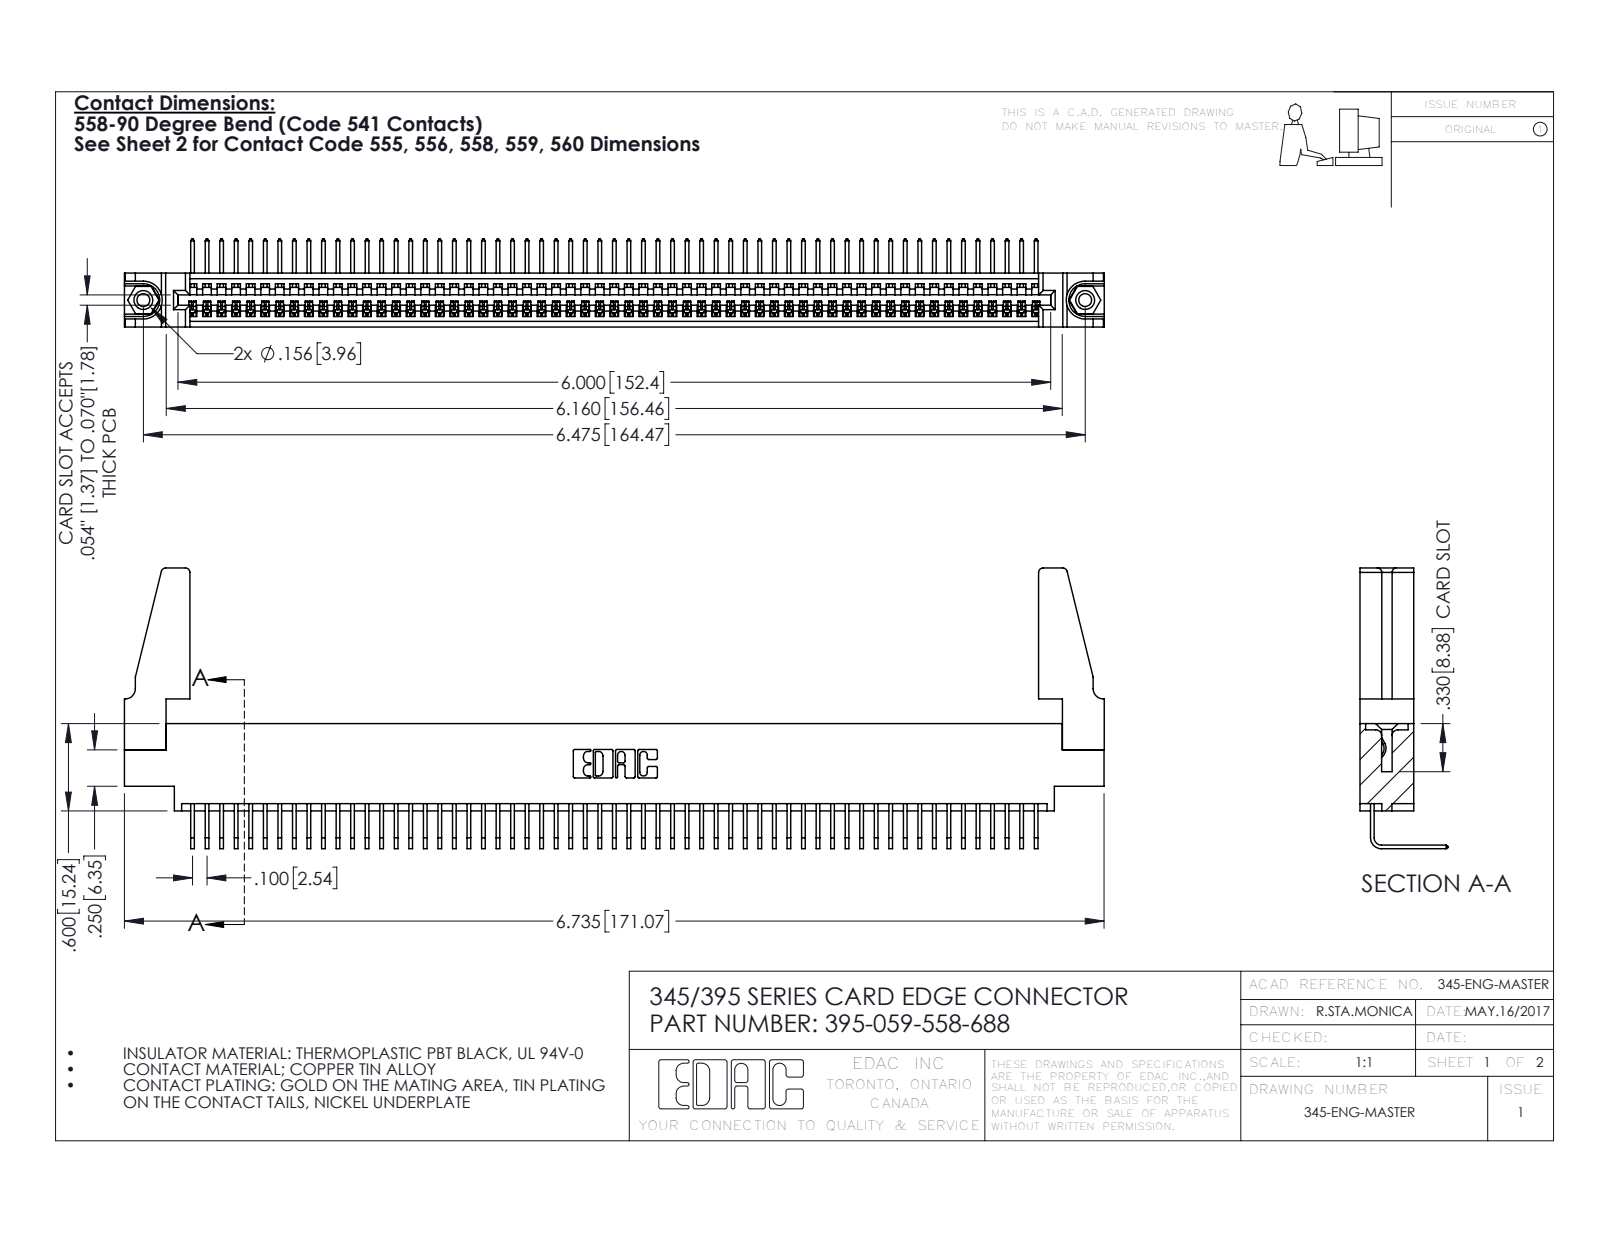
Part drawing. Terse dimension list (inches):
name: 345-292-001_558 Tail - 2; 395-059-558-688; 345-250-001_345-250-001-102; 345 Part_0.170 Offset - 0.156 Dia-TH (+1 more)
written by: SolidWorks 2016 (CONFIG_CONTROL_DESIGN)
unit: in
bodies: 64 solids, 3794 faces (2634 planar, 1144 cylindrical, 16 other)
size: 6.736 × 1.929 × 0.605
volume: 1.204 in³; area: 41.13 in²
holes: 2× ⌀0.089, 2× ⌀0.125, 2× ⌀0.156, 1× ⌀0.064
bosses: 2× ⌀0.155
rounds: 118× R0.006, 22× R0.01, 8× R0.03, 6× R0.007, 6× R0.031, 3× R0.026, 2× R0.031, 2× R0.04
face distances: 0.072, 0.298, 0.37, 0.098, 0.272, 0.025, 0.2, 0.225, 0.175, 0.149
hole spacings: 0.27, 6.239, 6.475
